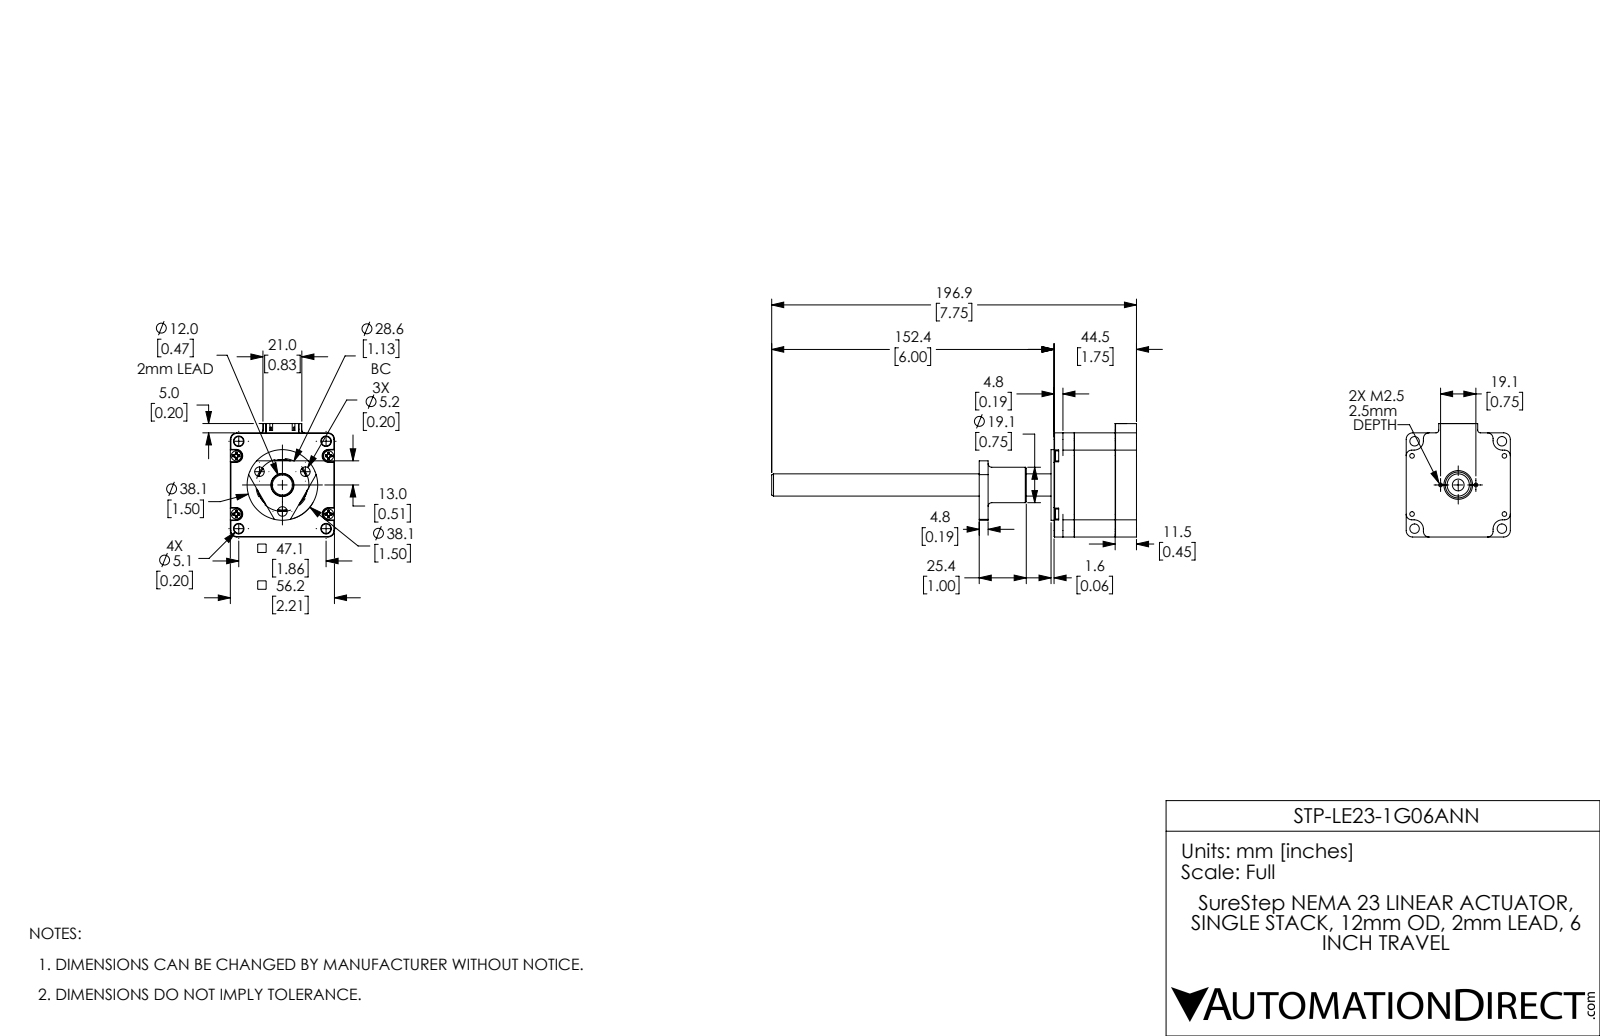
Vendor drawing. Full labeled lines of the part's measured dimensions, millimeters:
Part name (STEP PRODUCT): STP-LE23-1G06ANN; STP-LE23-1G06ANN_2; STP-LE23-1G06ANN_1
STEP written by: SolidWorks 2017 (AUTOMOTIVE_DESIGN)
Units: millimetres
Bodies: 8 solids, 712 faces (282 planar, 199 cylindrical, 231 other)
Overall size (bounding box): 196.9 × 61.22 × 56.2
Volume: 124 171 mm³ · Surface area: 50 152 mm²
Round holes (diameter × count): ⌀4.5 ×8, ⌀2.5 ×4, ⌀3.3 ×4, ⌀5.1 ×4, ⌀5.16 ×3, ⌀2 ×2, ⌀2.05 ×2, ⌀6.35 ×1, ⌀6.8 ×1, ⌀10.5 ×1, ⌀15.5 ×1, ⌀20 ×1
Round bosses / shafts (diameter × count): ⌀5.4 ×4, ⌀38.1 ×1, ⌀36 ×1, ⌀35.6 ×1, ⌀34.85 ×1, ⌀19.1 ×1, ⌀16 ×1, ⌀12 ×1
Partial cylindrical surfaces — rounded edges, fillets, slot ends (radius × count): R1.5 ×10, R3 ×8, R1.8 ×4, R3.2 ×4, R3.5 ×4, R5 ×4, R19.3 ×1
Main face-to-face distances: 22, 44.5, 56.2, 11.5, 33.5, 1.6, 51.4, 11, 33, 38.8
Hole centre spacings: 14.12, 24.75, 33.05, 35.01, 45.74, 48.53, 56.99, 6.55
